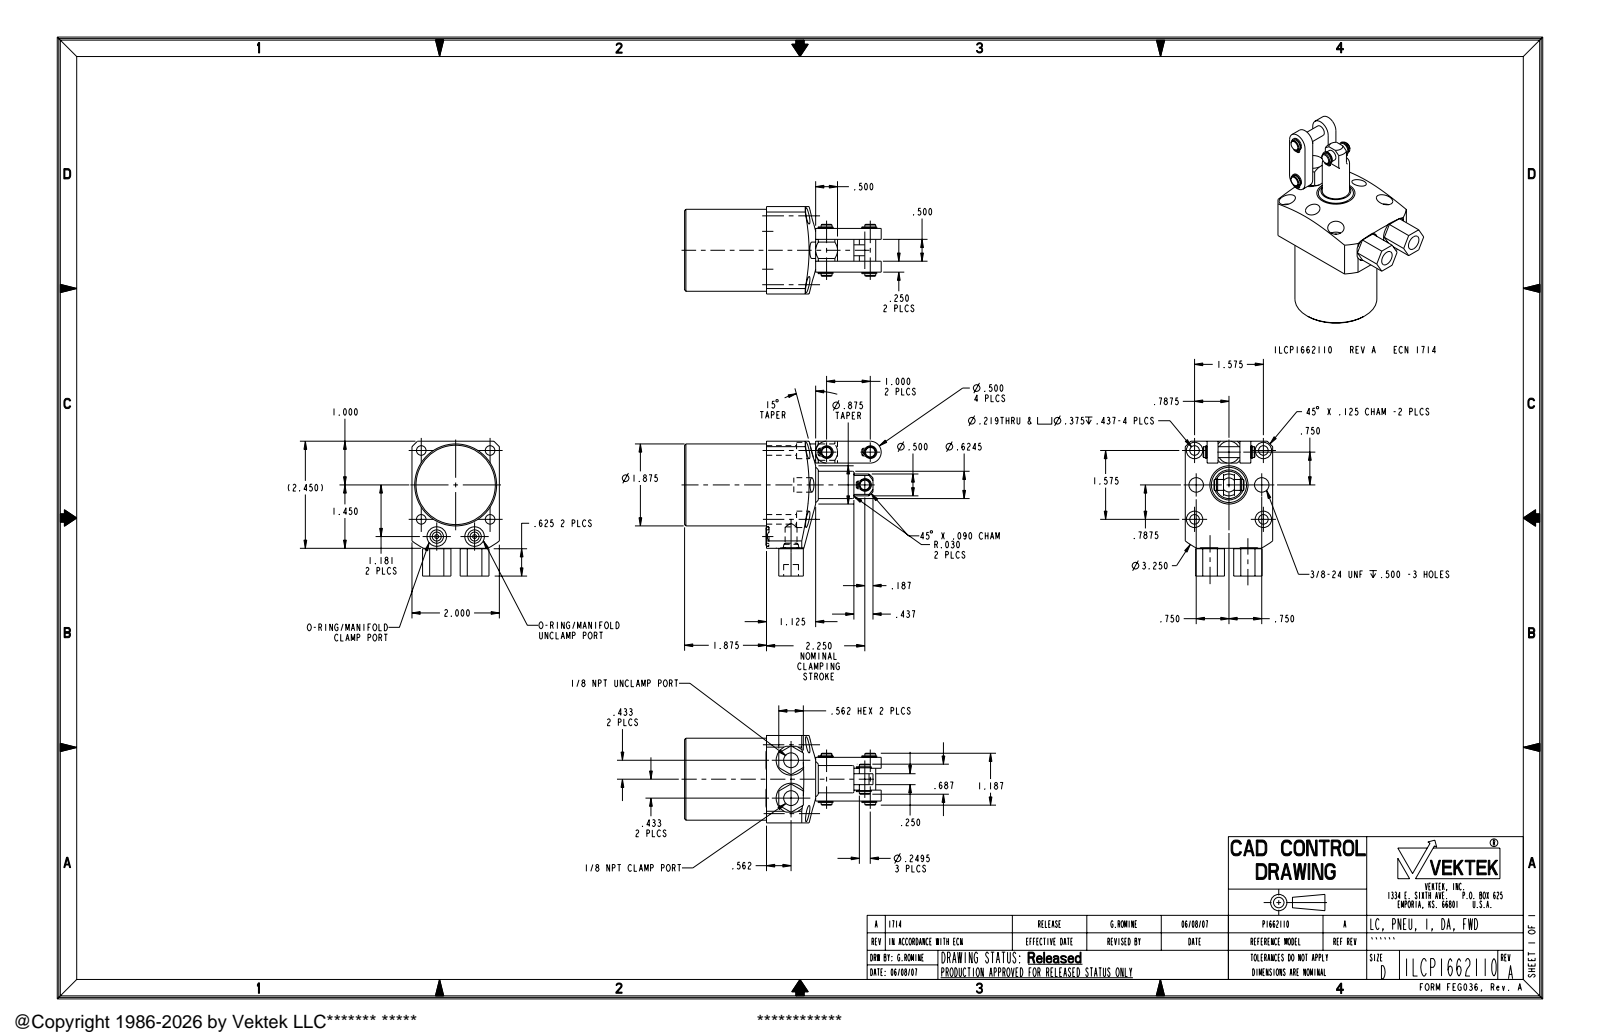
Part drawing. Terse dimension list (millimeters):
name: ILCP1662110
written by: PRO/ENGINEER BY PARAMETRIC TECHNOLOGY CORPORATION, 2005180 (AUTOMOTIVE_DESIGN_CC2)
unit: mm
bodies: 3 solids, 304 faces (120 planar, 132 cylindrical, 52 other)
size: 114.3 × 78.4 × 50.8
volume: 177 800 mm³; area: 30 150 mm²
holes: 6× ⌀1, 4× ⌀5.6, 4× ⌀9.5, 2× ⌀6.9, 2× ⌀8.4, 2× ⌀8.6, 2× ⌀11.4
bosses: 3× ⌀6.4, 2× ⌀7.9, 1× ⌀47.6, 1× ⌀15.8, 1× ⌀9.5
rounds: 12× R1, 3× R3.7, 3× R6.4, 2× R8.7, 1× R8, 1× R41.3
face distances: 12.7, 50.8, 19.1, 47.6, 38.1, 6.4, 31.8, 14.3, 25.4, 62.2
hole spacings: 20, 40, 43.9, 2.5, 13.5, 19.3, 22, 25.4
